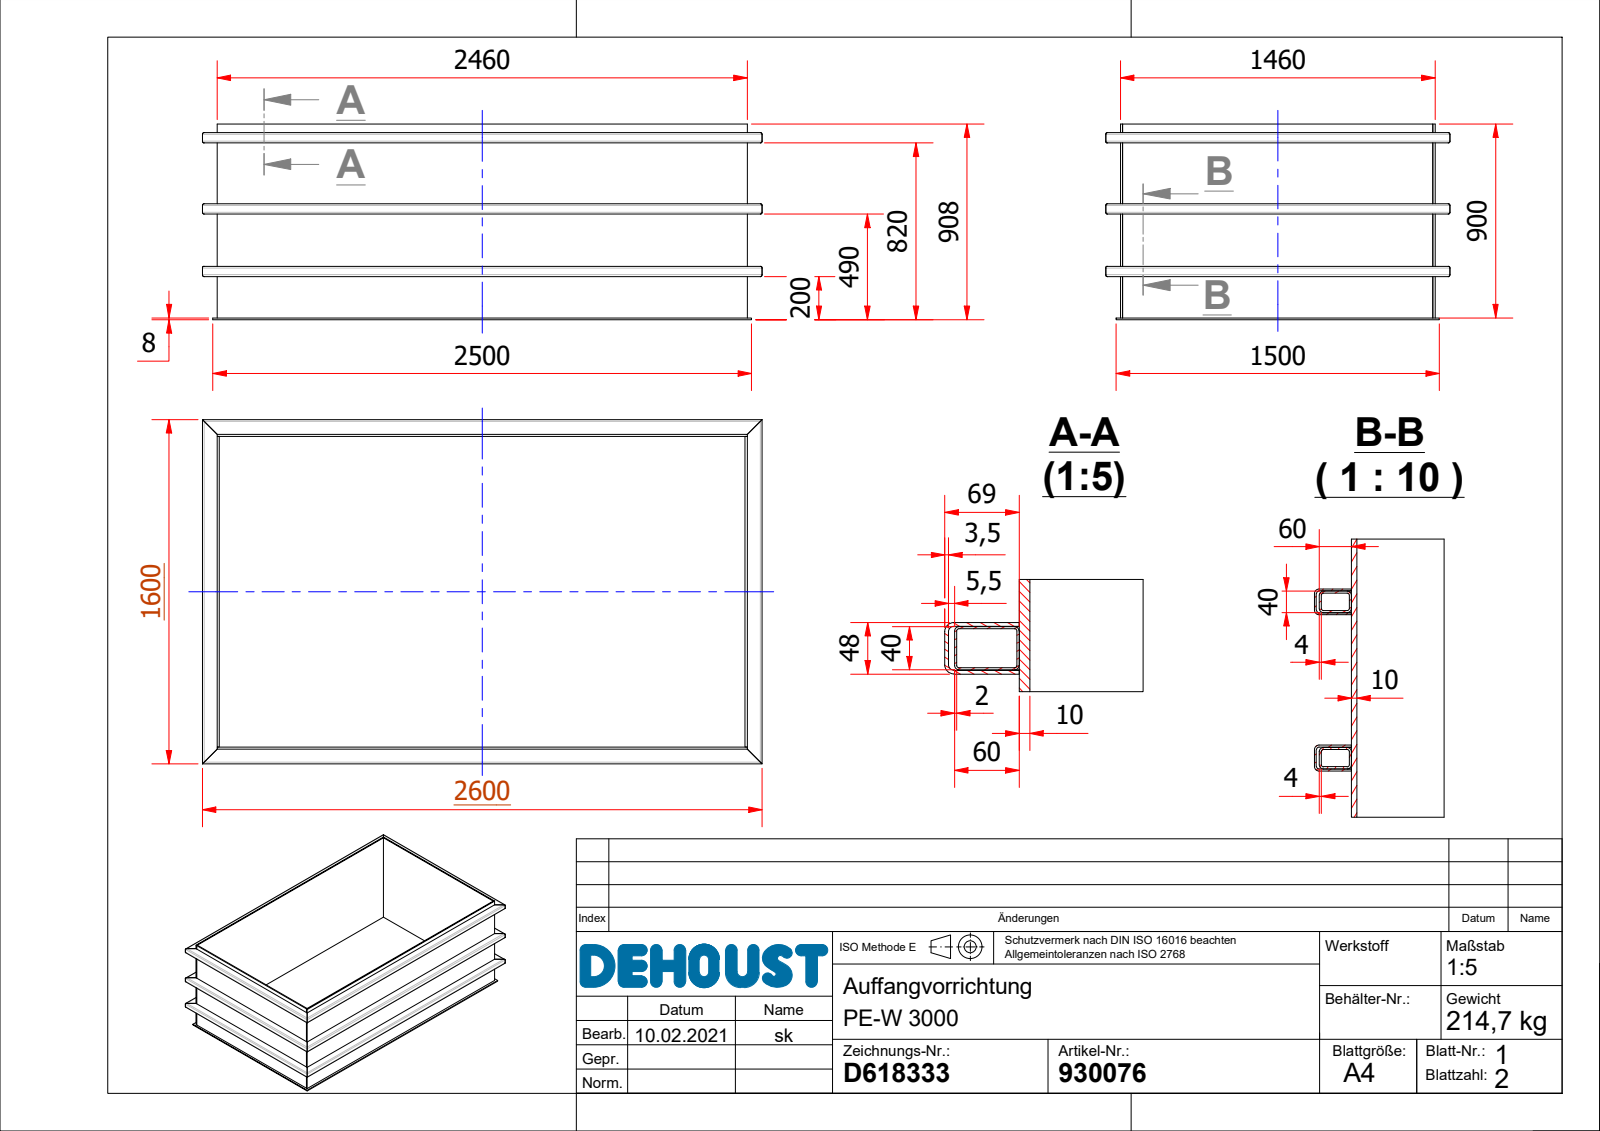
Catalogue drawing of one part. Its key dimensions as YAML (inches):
part_name: "D618333-0_-Auffangvorrichtung_3000; D618340-0_-Bodenplatte; D618341-0_-Längsseite; D618342-0_-Querseiite (+6 more)"
step_written_by: "Autodesk Inventor 2019 (AUTOMOTIVE_DESIGN)"
units: inches
bodies: {solids: 29, faces: 414, planar: 270, cylindrical: 144, other: 0}
overall_size: [102.283, 62.913, 35.748]
volume: 7890
surface_area: 60700
partial_cylinders:
  - {radius: 0.157, count: 48}
  - {radius: 0.315, count: 32}
  - {radius: 0.197, count: 24}
  - {radius: 0.335, count: 24}
  - {radius: 0.079, count: 16}
face_to_face_distances: [0.394, 57.087, 0.315, 0.138, 1.752, 11.417, 12.992, 96.457, 57.48, 0.157]
